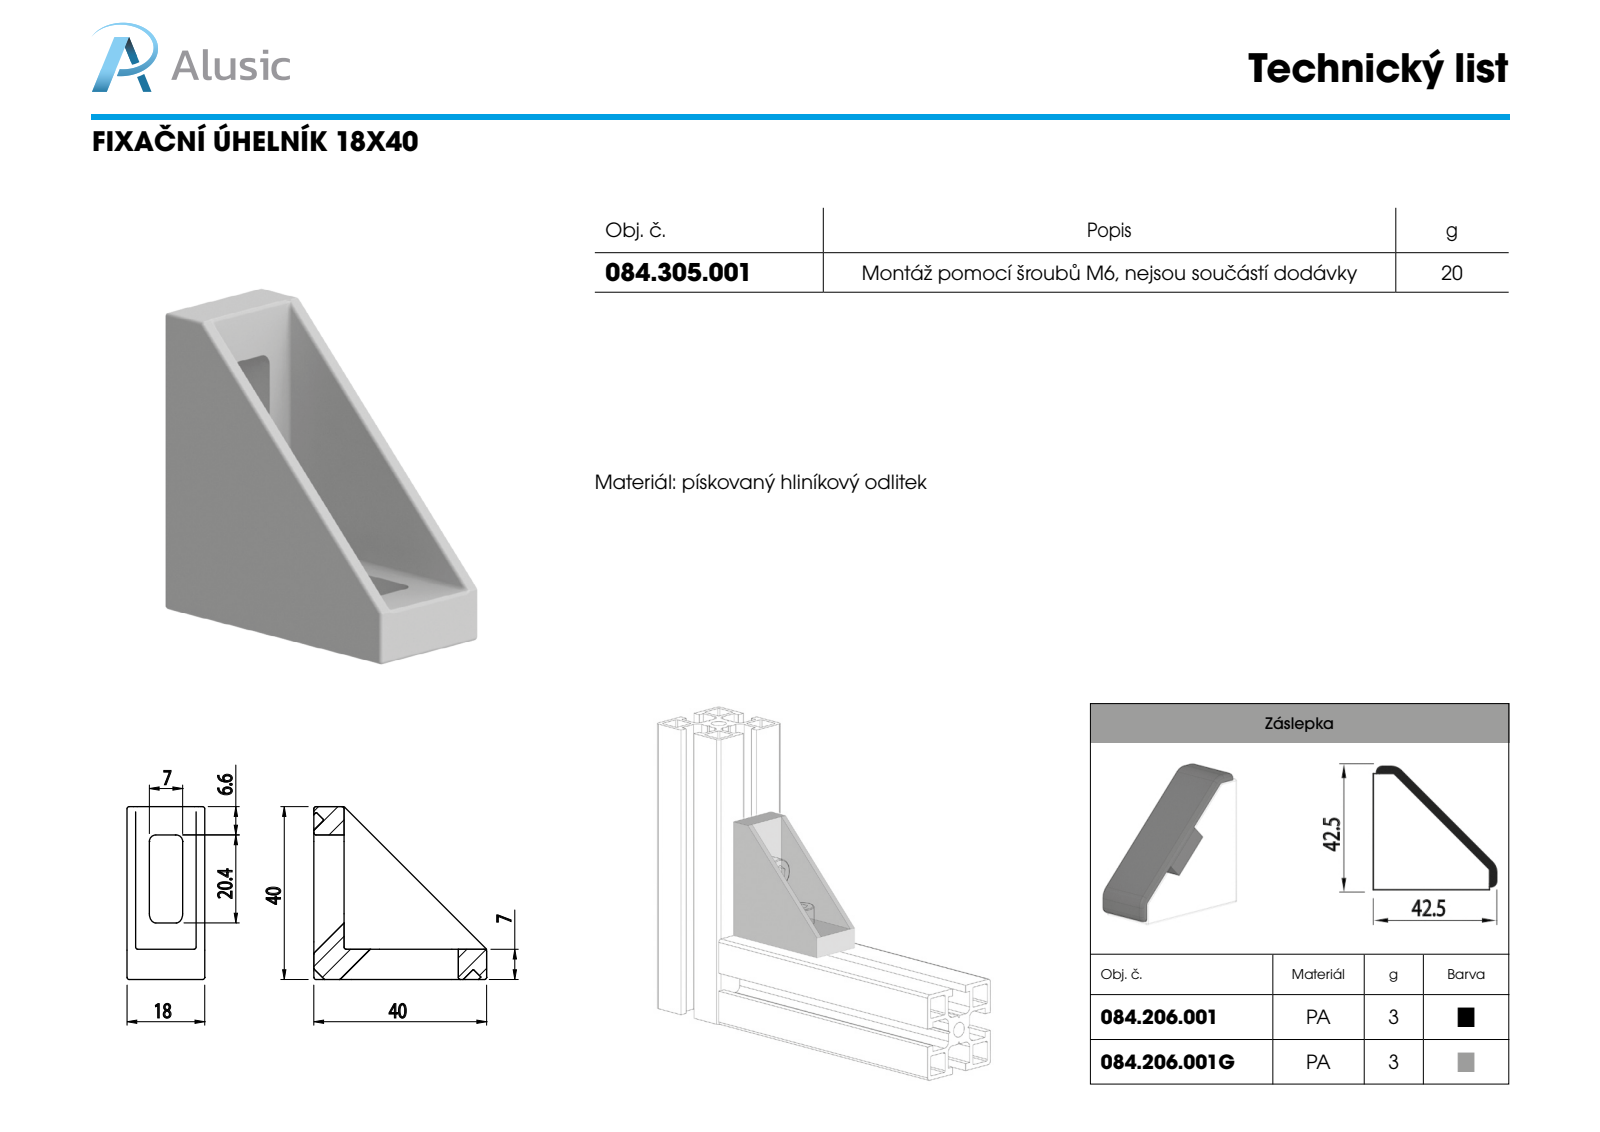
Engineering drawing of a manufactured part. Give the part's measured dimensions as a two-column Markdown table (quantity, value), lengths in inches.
| quantity | value |
| --- | --- |
| part name | 084.305.001-1 |
| STEP written by | SolidWorks 2016 (CONFIG_CONTROL_DESIGN) |
| units | inches |
| bodies | 1 solid, 144 faces (33 planar, 69 cylindrical, 42 other) |
| overall size | 1.575 × 1.575 × 0.709 |
| volume | 0.544 in³ |
| surface area | 9.467 in² |
| partial cylindrical surfaces (radius × count) | 0.02 × 32, 0.008 × 23, 0.059 × 8 |
| main face-to-face distances | 0.709, 0.079, 0.63, 0.276, 0.217, 0.492, 0.138, 0.413, 0.551, 1.299 |
